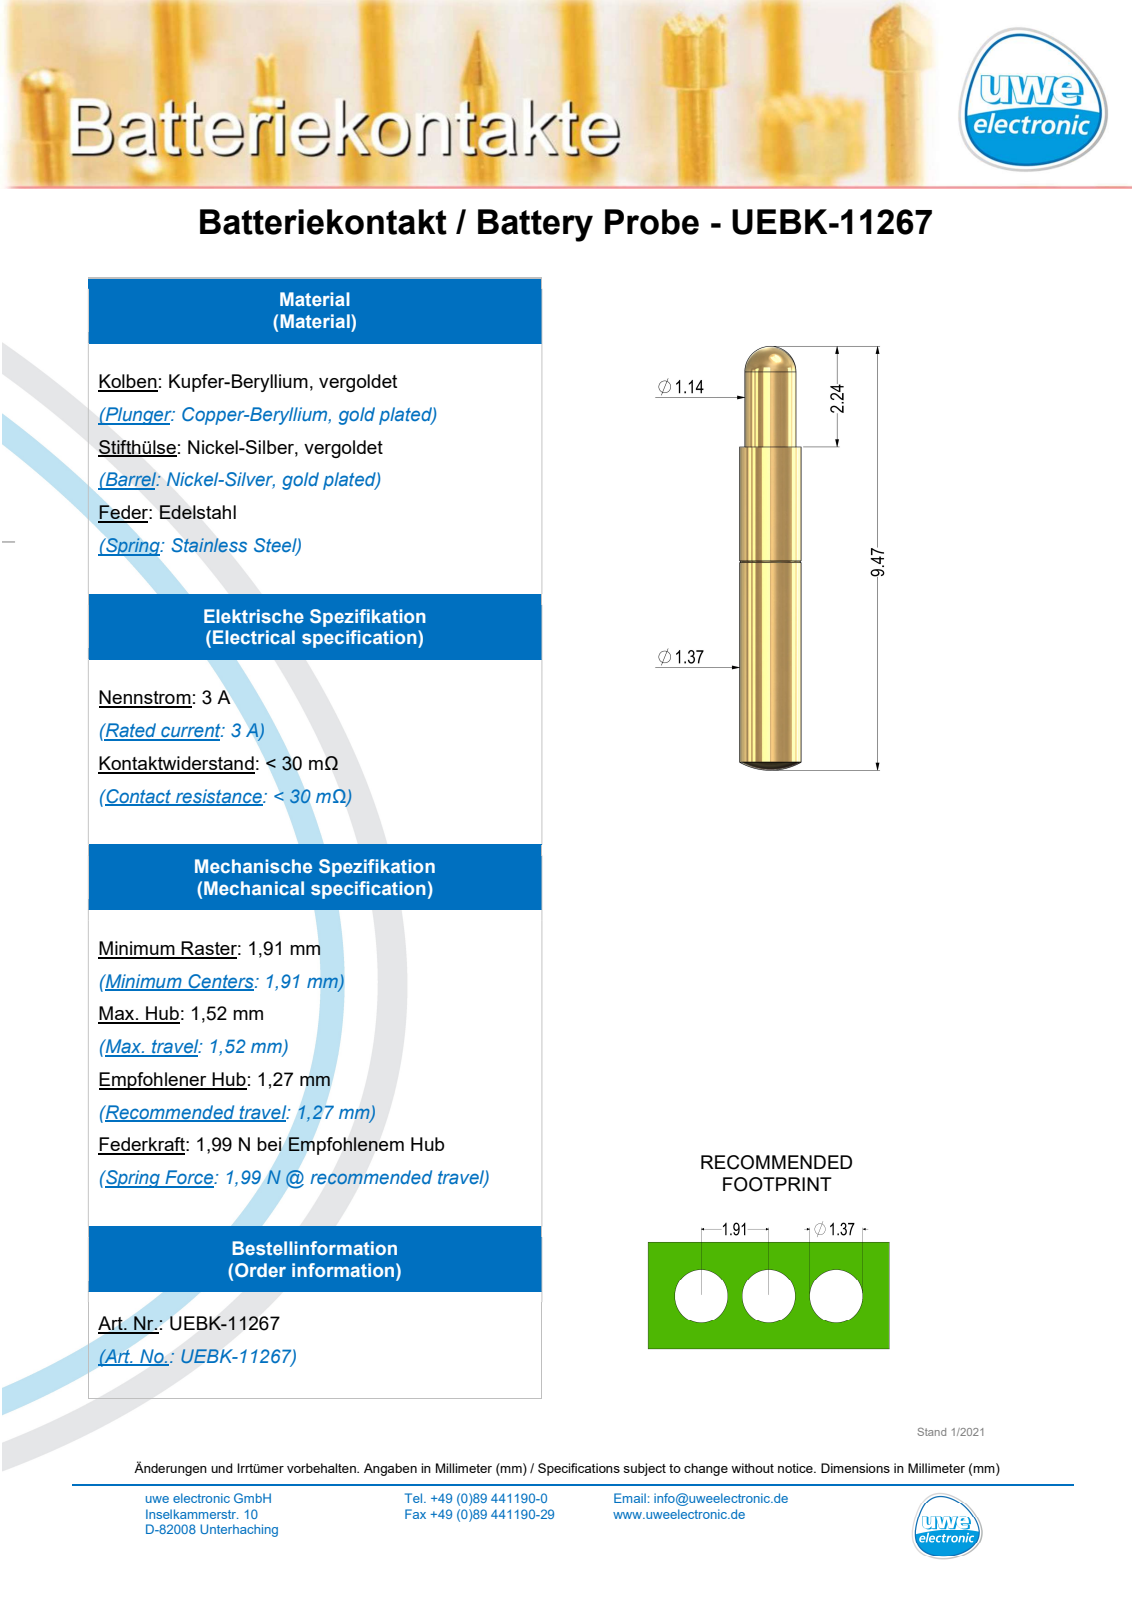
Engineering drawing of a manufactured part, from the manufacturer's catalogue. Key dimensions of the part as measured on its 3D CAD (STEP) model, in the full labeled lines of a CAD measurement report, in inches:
Part name (STEP PRODUCT): UEBK-11267
STEP written by: SolidWorks 2016 (AUTOMOTIVE_DESIGN)
Units: inches
Bodies: 1 solid, 15 faces (1 planar, 6 cylindrical, 8 other)
Overall size (bounding box): 0.373 × 0.054 × 0.054
Volume: 0.001 in³ · Surface area: 0.062 in²
Round bosses / shafts (diameter × count): ⌀0.054 ×1, ⌀0.045 ×1
